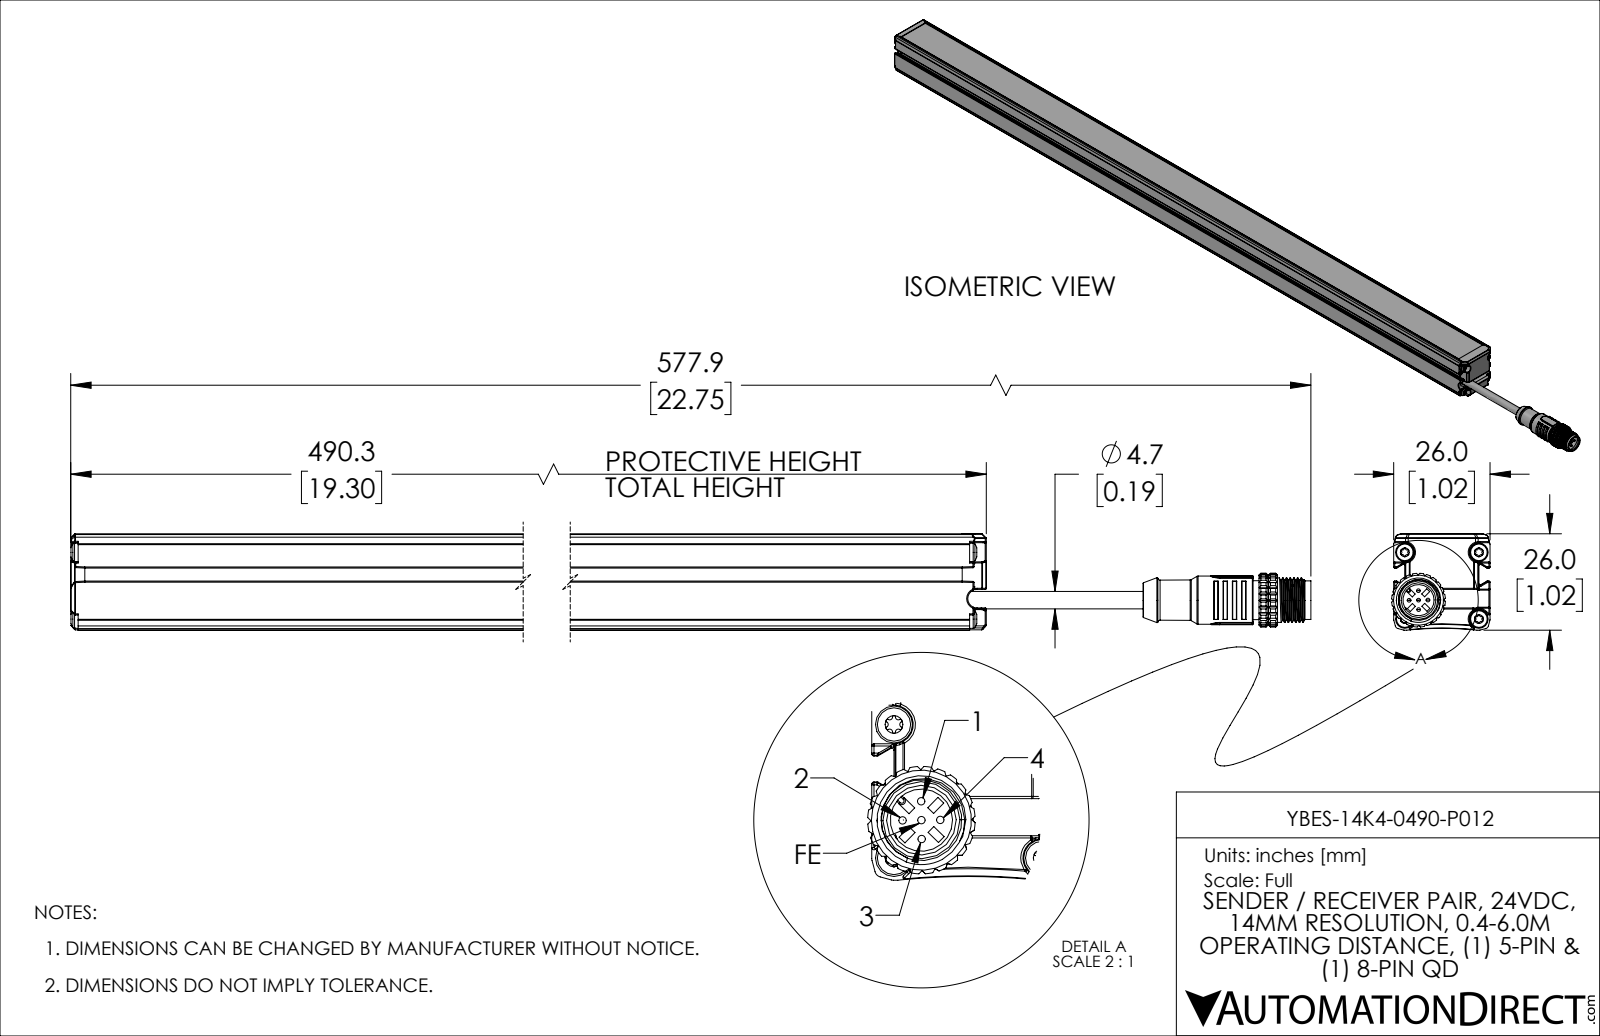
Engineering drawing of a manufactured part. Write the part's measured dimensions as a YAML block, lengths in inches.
part_name: "YBES-14K4-0490-P012_REV1"
step_written_by: "SolidWorks 2019 (AUTOMOTIVE_DESIGN)"
units: inches
bodies: {solids: 2, faces: 1937, planar: 729, cylindrical: 727, other: 481}
overall_size: [22.752, 1.045, 1.024]
volume: 7.222
surface_area: 199.8
round_holes:
  - {diameter: 0.094, count: 4}
  - {diameter: 0.1, count: 4}
  - {diameter: 0.146, count: 4}
  - {diameter: 0.197, count: 4}
  - {diameter: 0.189, count: 1}
  - {diameter: 0.232, count: 1}
  - {diameter: 0.331, count: 1}
  - {diameter: 0.354, count: 1}
  - {diameter: 0.376, count: 1}
round_bosses_or_shafts:
  - {diameter: 0.039, count: 5}
  - {diameter: 0.035, count: 5}
  - {diameter: 0.126, count: 4}
  - {diameter: 0.098, count: 4}
  - {diameter: 0.051, count: 4}
  - {diameter: 0.059, count: 2}
  - {diameter: 0.531, count: 1}
  - {diameter: 0.512, count: 1}
partial_cylinders:
  - {radius: 0.008, count: 153}
  - {radius: 0.012, count: 115}
  - {radius: 0.008, count: 24}
  - {radius: 0.015, count: 24}
  - {radius: 0.039, count: 18}
  - {radius: 0.016, count: 16}
  - {radius: 0.006, count: 10}
  - {radius: 0.02, count: 7}
face_to_face_distances: [0.118, 0.059, 0.071, 0.835, 1.024, 0.717, 0.047, 0.016, 0.906, 0.189]
hole_center_spacings: [0.709, 0.787, 1.059, 0.248, 0.528, 0.672, 0.819]
